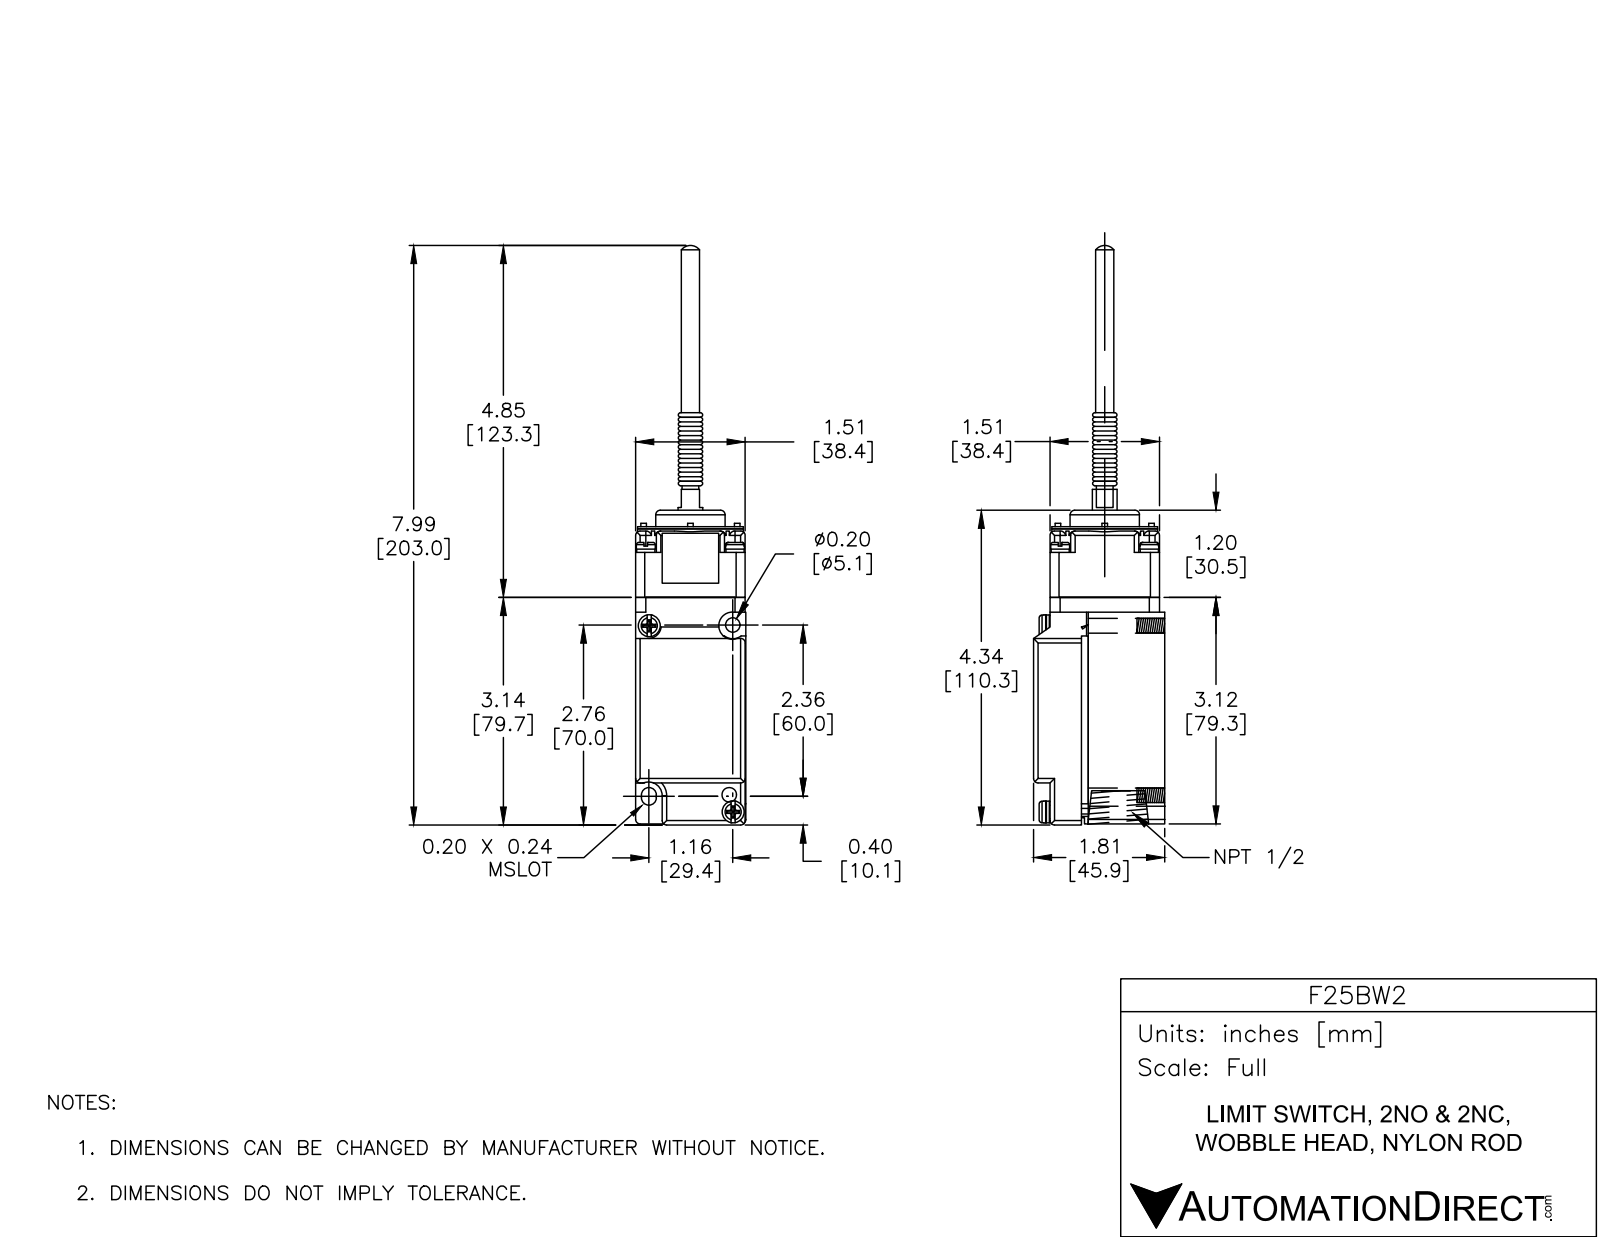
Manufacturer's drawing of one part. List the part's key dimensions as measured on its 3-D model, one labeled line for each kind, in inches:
Part name (STEP PRODUCT): F25BW2
STEP written by: SolidWorks 2018 (AUTOMOTIVE_DESIGN)
Units: inches
Bodies: 35 solids, 899 faces (264 planar, 140 cylindrical, 495 other)
Overall size (bounding box): 7.992 × 1.809 × 1.52
Volume: 10.15 in³ · Surface area: 79.64 in²
Round holes (diameter × count): ⌀0.077 ×4, ⌀0.177 ×4, ⌀0.19 ×3, ⌀0.2 ×3, ⌀0.23 ×1, ⌀0.92 ×1, ⌀1.054 ×1
Round bosses / shafts (diameter × count): ⌀0.25 ×5, ⌀0.26 ×4, ⌀0.14 ×4, ⌀0.302 ×2, ⌀0.3 ×2, ⌀1.458 ×1, ⌀0.956 ×1, ⌀0.4 ×1
Partial cylindrical surfaces — rounded edges, fillets, slot ends (radius × count): R0.062 ×21, R0.03 ×16, R0.015 ×8, R0.062 ×8, R0.14 ×4, R0.145 ×4, R0.102 ×2, R0.188 ×2
Main face-to-face distances: 0.094, 1.149, 1.055, 1.52, 0.945, 0.66, 0.754, 1.809, 1.51, 0.227
Hole centre spacings: 1.403, 0.616, 0.646, 0.616, 0.87, 0.87, 0.913, 0.914
